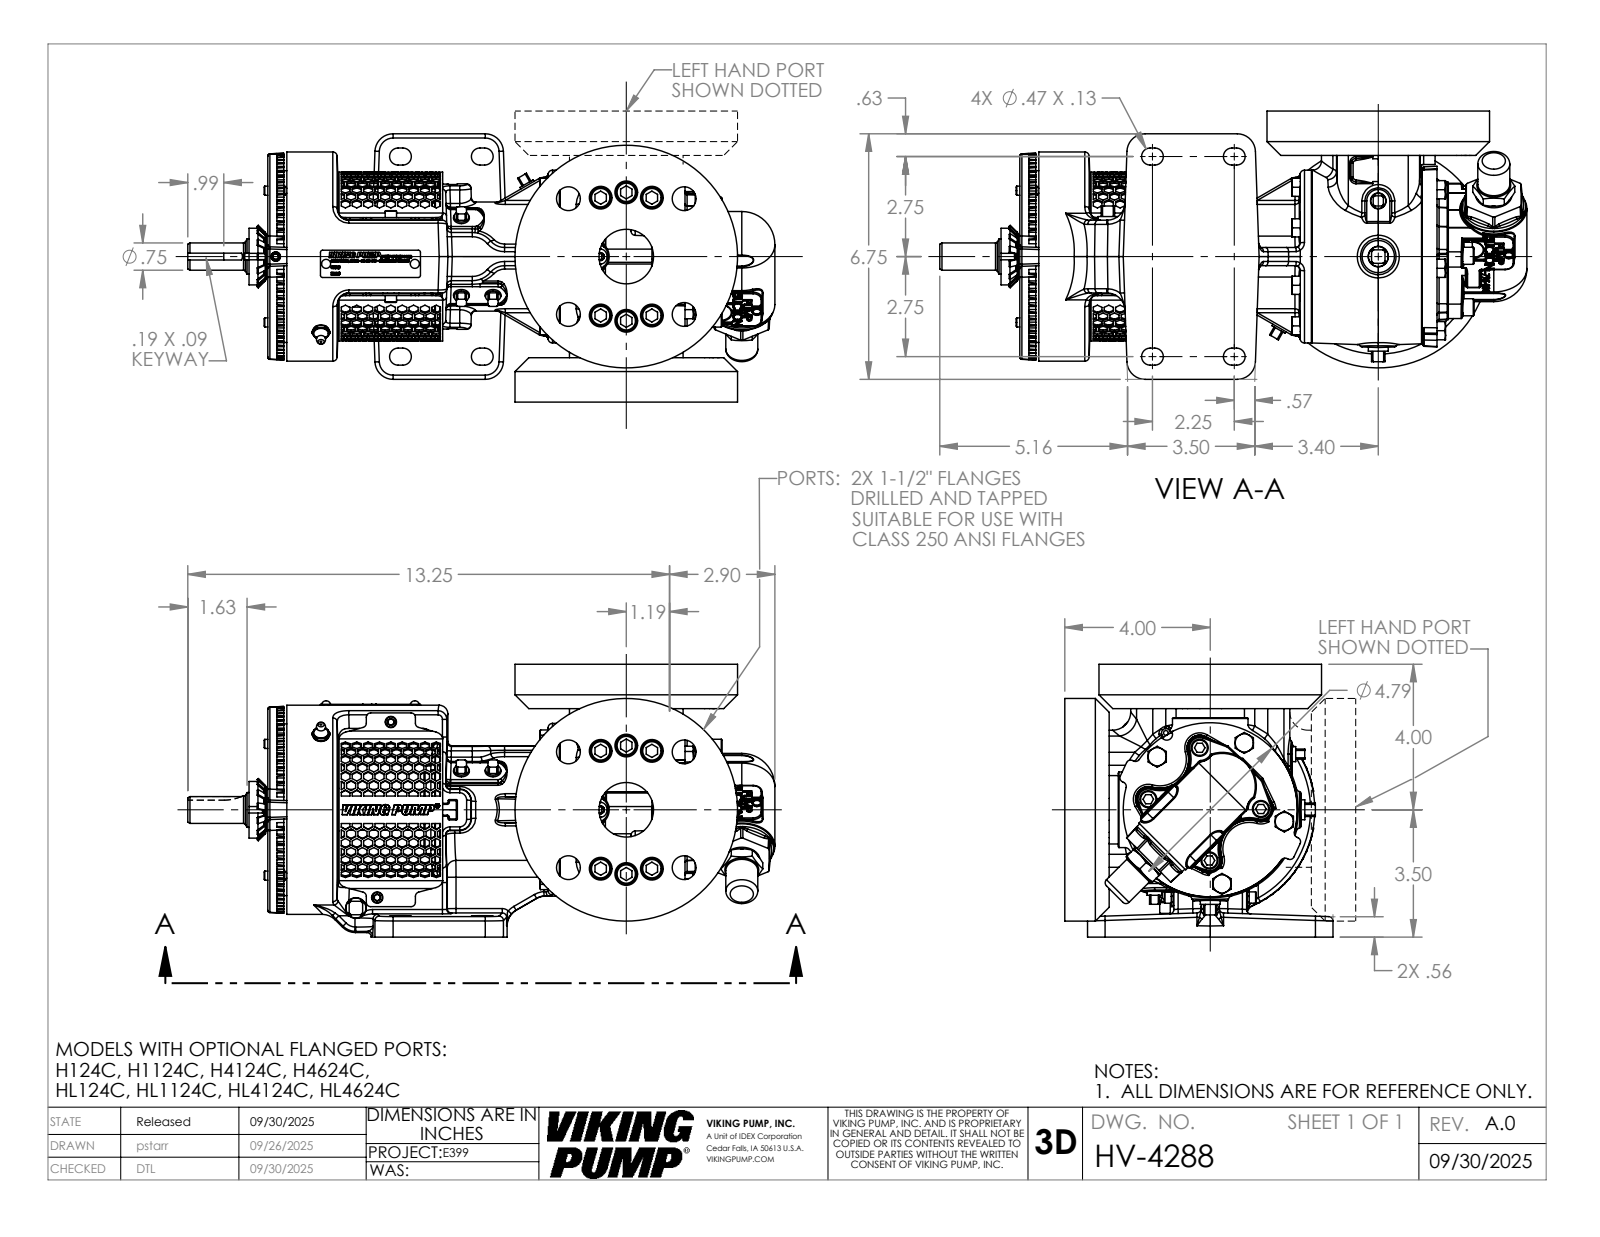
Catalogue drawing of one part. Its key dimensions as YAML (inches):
part_name: "HV-4288"
step_written_by: "SolidWorks 2024 (AUTOMOTIVE_DESIGN)"
units: inches
bodies: {solids: 1, faces: 5139, planar: 1875, cylindrical: 1026, other: 2238}
overall_size: [16.145, 7.5, 7.375]
volume: 259.6
surface_area: 683.5
round_holes:
  - {diameter: 0.25, count: 9}
  - {diameter: 0.625, count: 8}
  - {diameter: 0.656, count: 8}
  - {diameter: 0.34, count: 5}
  - {diameter: 0.344, count: 4}
  - {diameter: 0.625, count: 4}
  - {diameter: 0.159, count: 3}
  - {diameter: 0.198, count: 3}
  - {diameter: 0.257, count: 3}
  - {diameter: 1.5, count: 2}
  - {diameter: 0.344, count: 1}
  - {diameter: 0.985, count: 1}
round_bosses_or_shafts:
  - {diameter: 0.563, count: 12}
  - {diameter: 0.469, count: 4}
  - {diameter: 0.313, count: 4}
  - {diameter: 0.312, count: 3}
  - {diameter: 0.19, count: 3}
  - {diameter: 6.12, count: 2}
  - {diameter: 0.25, count: 2}
  - {diameter: 5.75, count: 1}
partial_cylinders:
  - {radius: 0.054, count: 140}
  - {radius: 0.12, count: 104}
  - {radius: 0.03, count: 94}
  - {radius: 0.06, count: 54}
  - {radius: 0.5, count: 34}
  - {radius: 0.24, count: 11}
  - {radius: 0.234, count: 8}
  - {radius: 0.25, count: 8}
face_to_face_distances: [7.5, 1.22, 1.94, 6.28, 11.474, 9.533, 0.524, 1.417, 10.95, 1.5]
hole_center_spacings: [1.766, 2.56, 0.719, 0.887, 1.6, 2.25, 2.295, 3.182]
